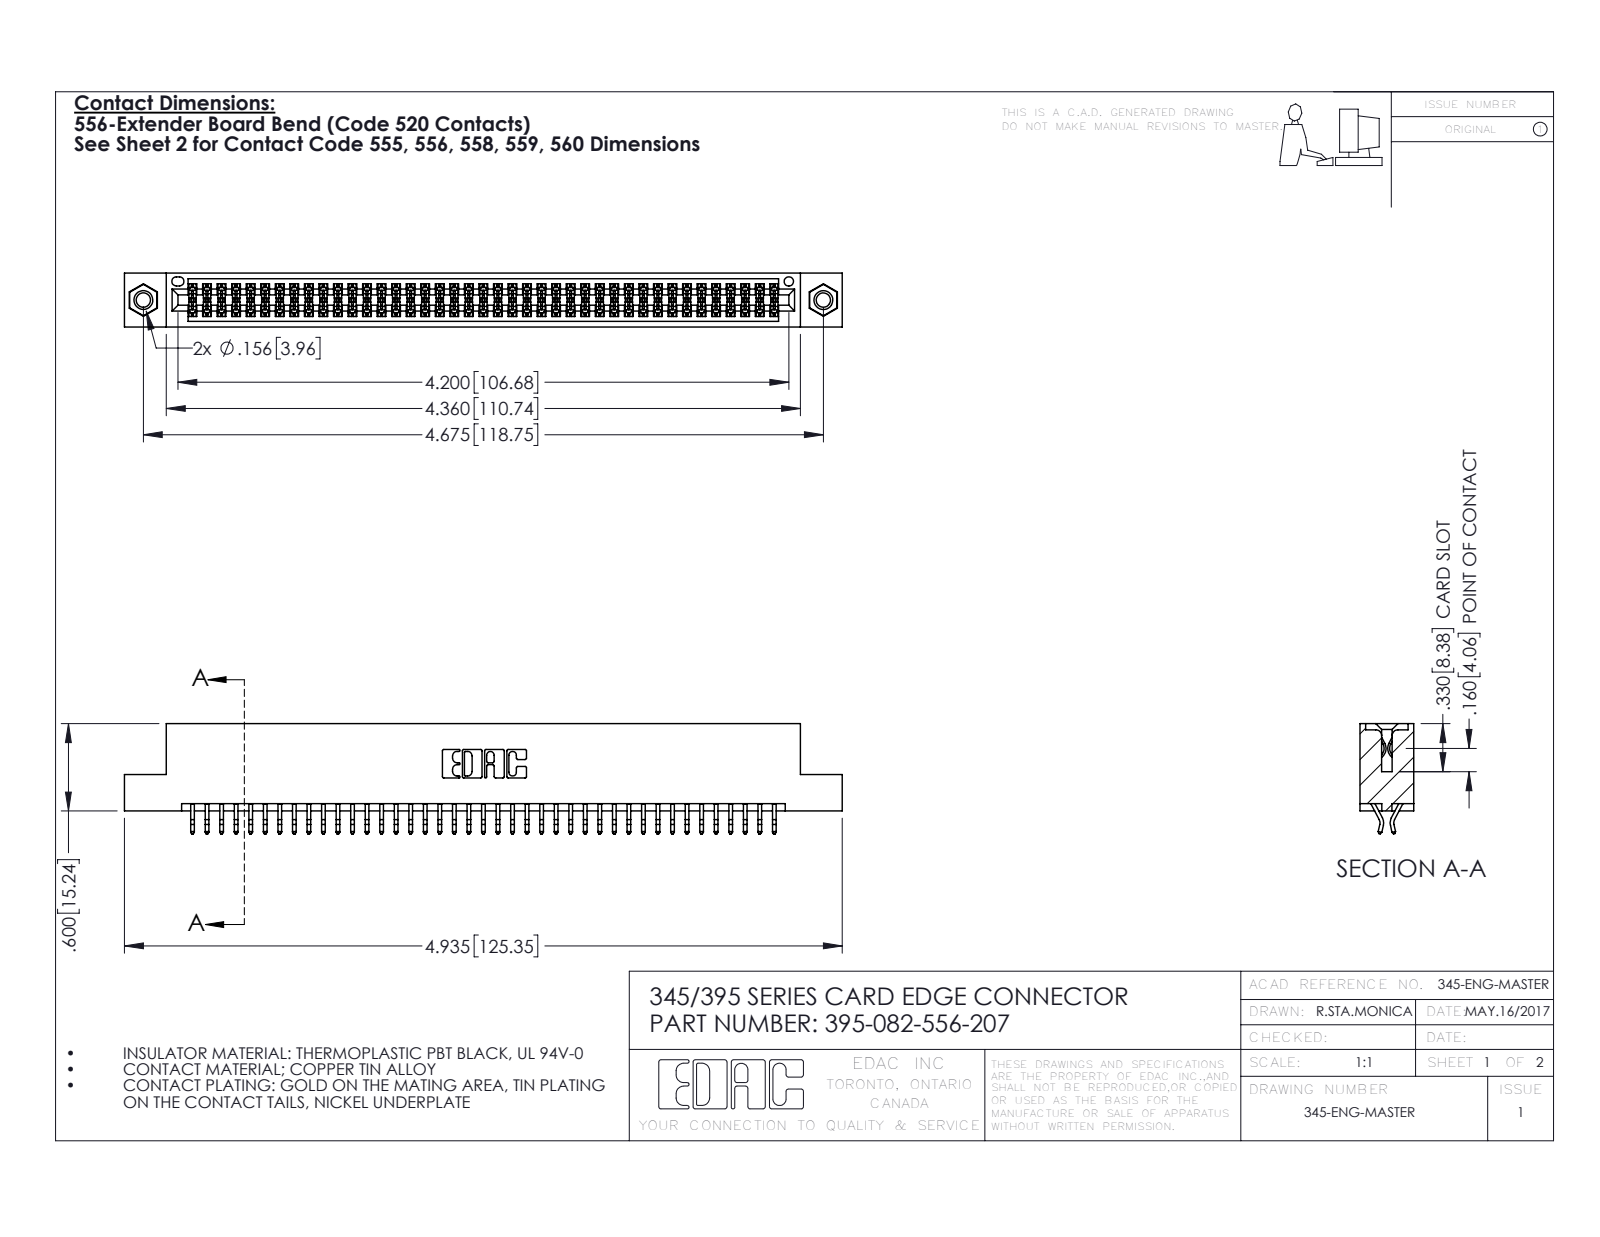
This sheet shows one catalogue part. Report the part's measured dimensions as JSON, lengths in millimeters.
{"part_name": "345-250-001_345-250-005-103; 345-292-001_556 Tail; 345 Part_Flush Mounting Lugs - 0.156 Dia-TI; 395-082-556-207", "step_written_by": "SolidWorks 2016 (CONFIG_CONTROL_DESIGN)", "units": "millimeters", "bodies": {"solids": 85, "faces": 4778, "planar": 3146, "cylindrical": 1616, "other": 16}, "overall_size": [125.3, 19.2, 9.4], "volume_mm3": 12100, "surface_area_mm2": 17900, "round_holes": [[2.5, 2], [3.2, 2], [4, 2], [1.6, 1]], "round_bosses_or_shafts": [[3.9, 2]], "partial_cylinders_radius": [[0.2, 123], [0.3, 22], [0.2, 6], [0.8, 6], [0.7, 3], [0.3, 2], [0.4, 2], [0.5, 2]], "face_to_face_distances": [1.8, 7.6, 9.4, 5.1, 0.6, 2.5, 6.9, 5.7, 4.4, 3.8], "hole_center_spacings": [6.9, 112.8, 118.7]}
